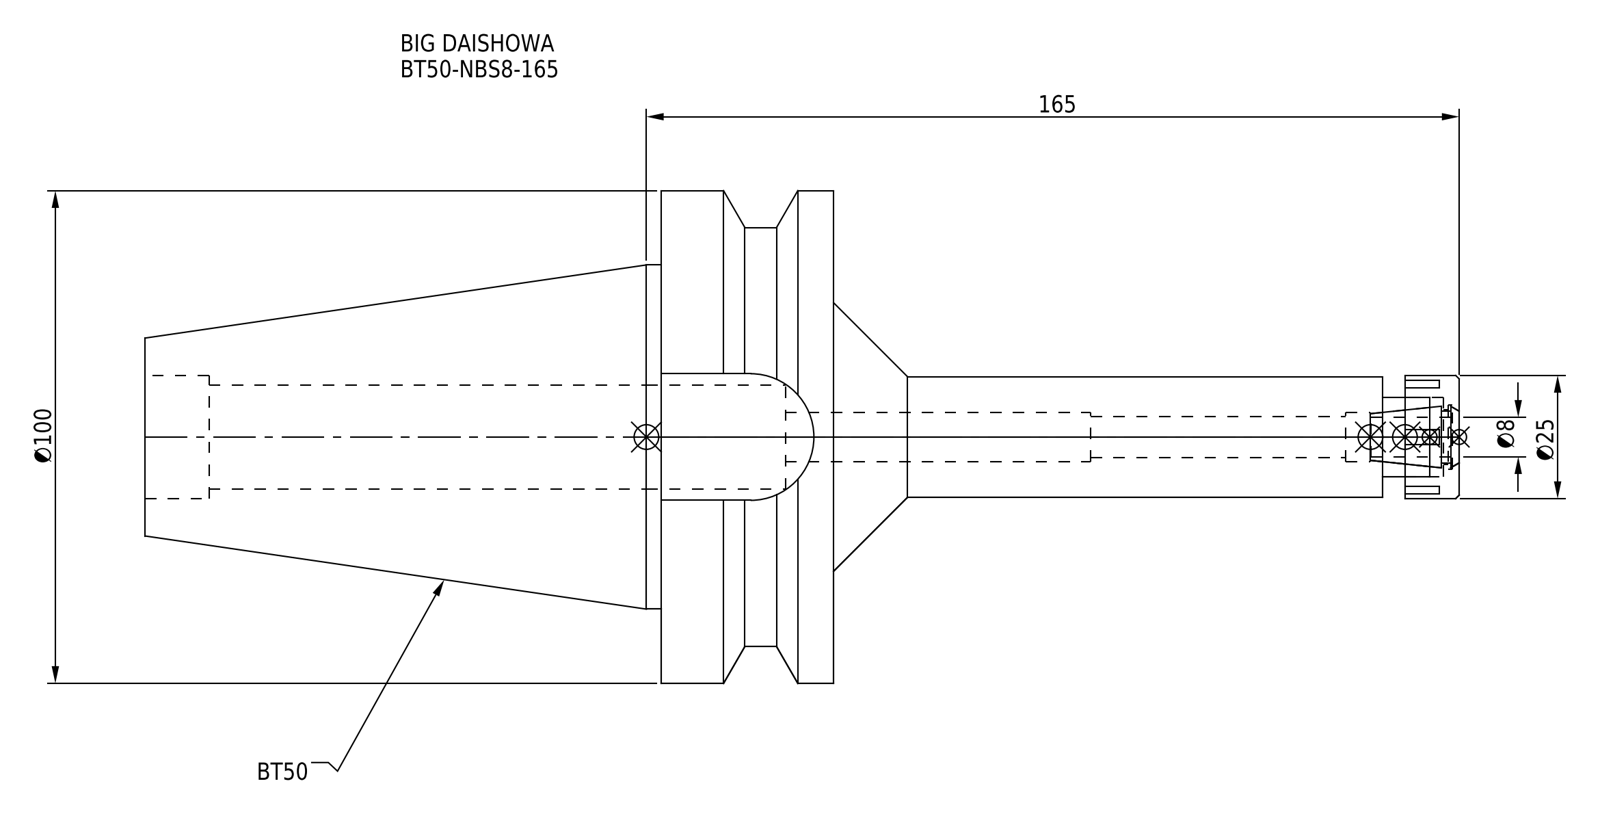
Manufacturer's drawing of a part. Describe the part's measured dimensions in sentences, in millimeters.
The part is named "BT50-NBS8-165-FreeParts; BT50-NBS8-165_1.stp; BT50NB08165-080_ASM.stp; BT50-NBS8-165 (+3 more)". Its 3-D file was written by "SolidWorks 2019 (CONFIG_CONTROL_DESIGN)". It is 2 solids with 93 faces: 45 planar, 34 cylindrical and 14 other. Overall it measures 266.8 by 100 by 100 millimeters. Its volume is 507 079 cubic millimeters and its surface area 68 688 square millimeters. Round holes: 1 of diameter 8.4, 1 of diameter 10, 1 of diameter 11, 1 of diameter 13, 1 of diameter 16, 1 of diameter 21.2, 1 of diameter 25. Round bosses or shafts: 1 of diameter 100, 1 of diameter 85, 1 of diameter 69.85, 1 of diameter 24.5. Partial cylindrical surfaces (rounded edges, fillets, slot ends): 1 of radius 12.85. The main face-to-face distances are 35, 139.8, 104.8, 70.8, 25.7, 127, 162, 266.8, 136.8, 9.8.
